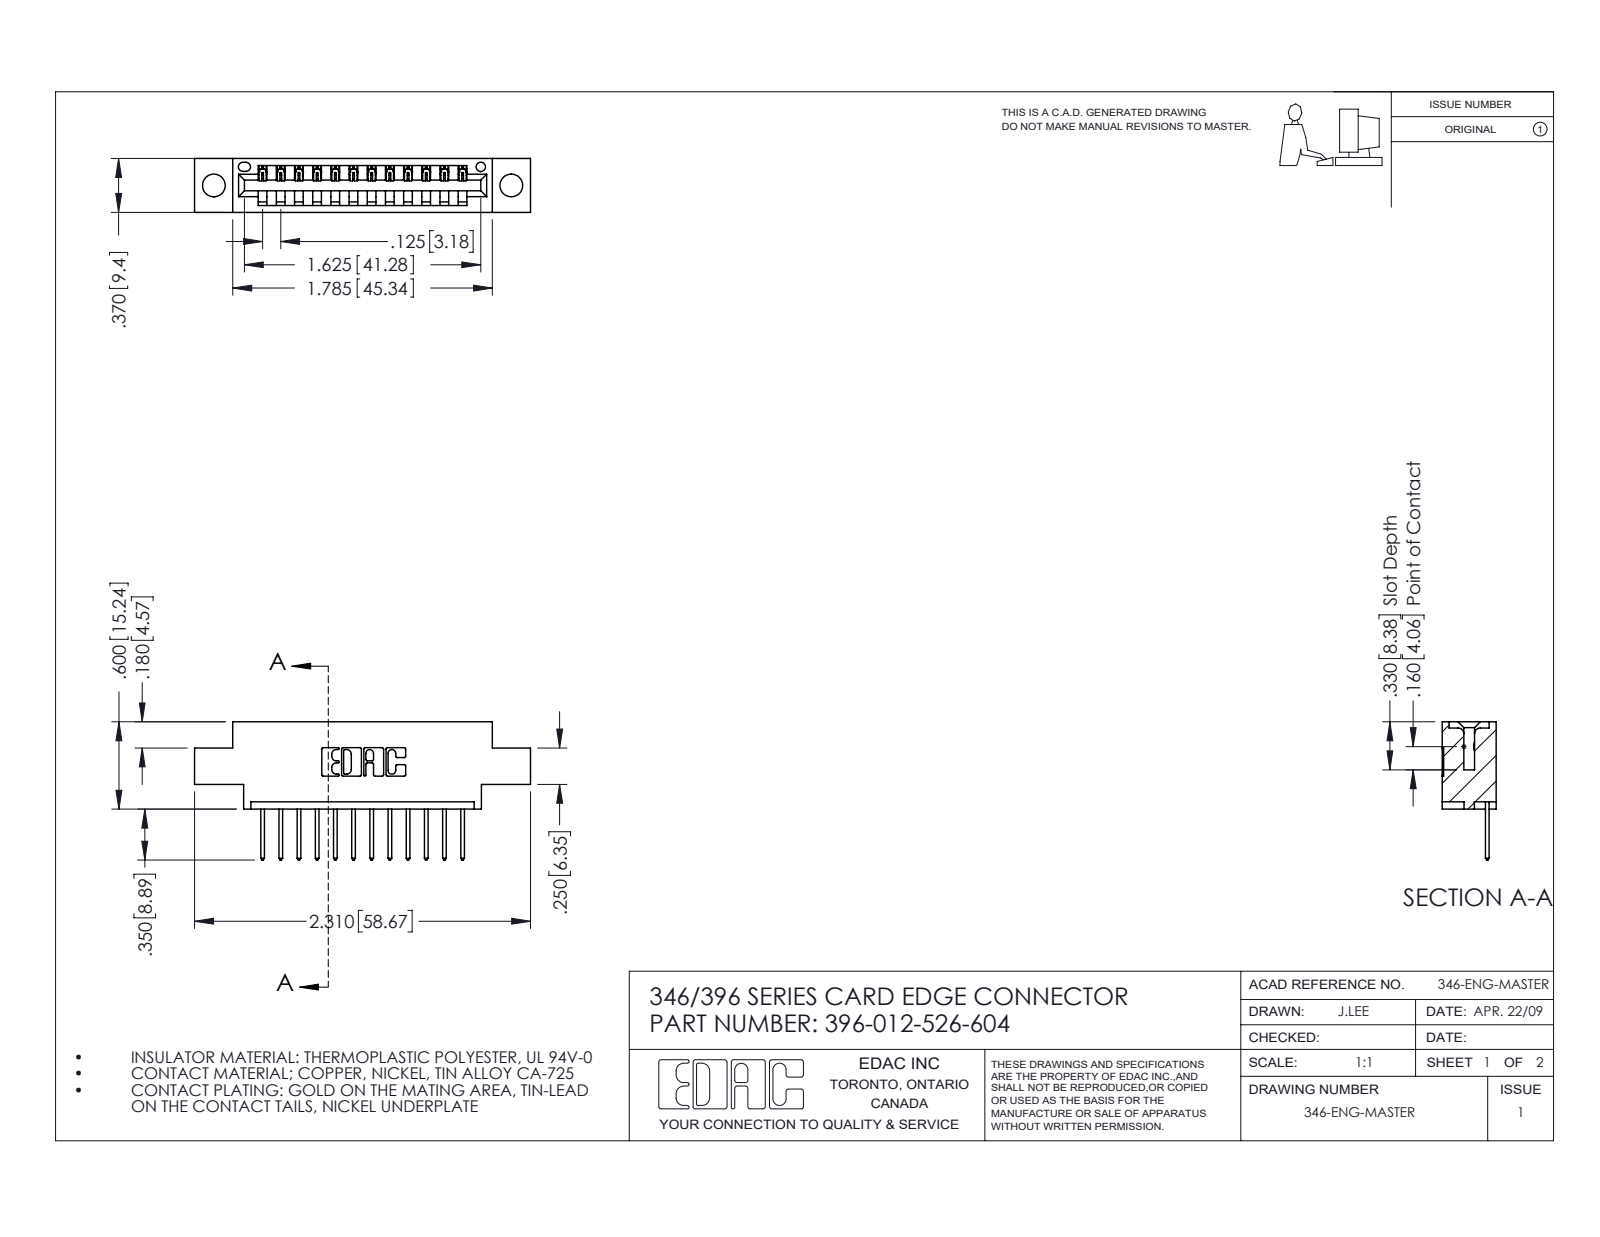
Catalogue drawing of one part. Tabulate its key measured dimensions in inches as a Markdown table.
| quantity | value |
| --- | --- |
| part name | 346 Part_0.170 Offset - 0.156 Dia-TH; 345-292-001_345-293-126; 396-012-526-604 |
| STEP written by | SolidWorks 2016 (CONFIG_CONTROL_DESIGN) |
| units | inches |
| bodies | 13 solids, 822 faces (560 planar, 262 cylindrical, 0 other) |
| overall size | 2.31 × 0.95 × 0.37 |
| volume | 0.315 in³ |
| surface area | 9.418 in² |
| round holes (diameter × count) | 0.156 × 2, 0.064 × 1 |
| partial cylindrical surfaces (radius × count) | 0.006 × 24, 0.01 × 24, 0.01 × 22, 0.007 × 6, 0.031 × 6, 0.026 × 3, 0.031 × 2, 0.04 × 2 |
| main face-to-face distances | 0.25, 0.37, 0.048, 0.322, 0.072, 0.298, 0.025, 0.148, 0.222, 0.1 |
| hole center spacings | 0.246, 1.839, 2.045 |
